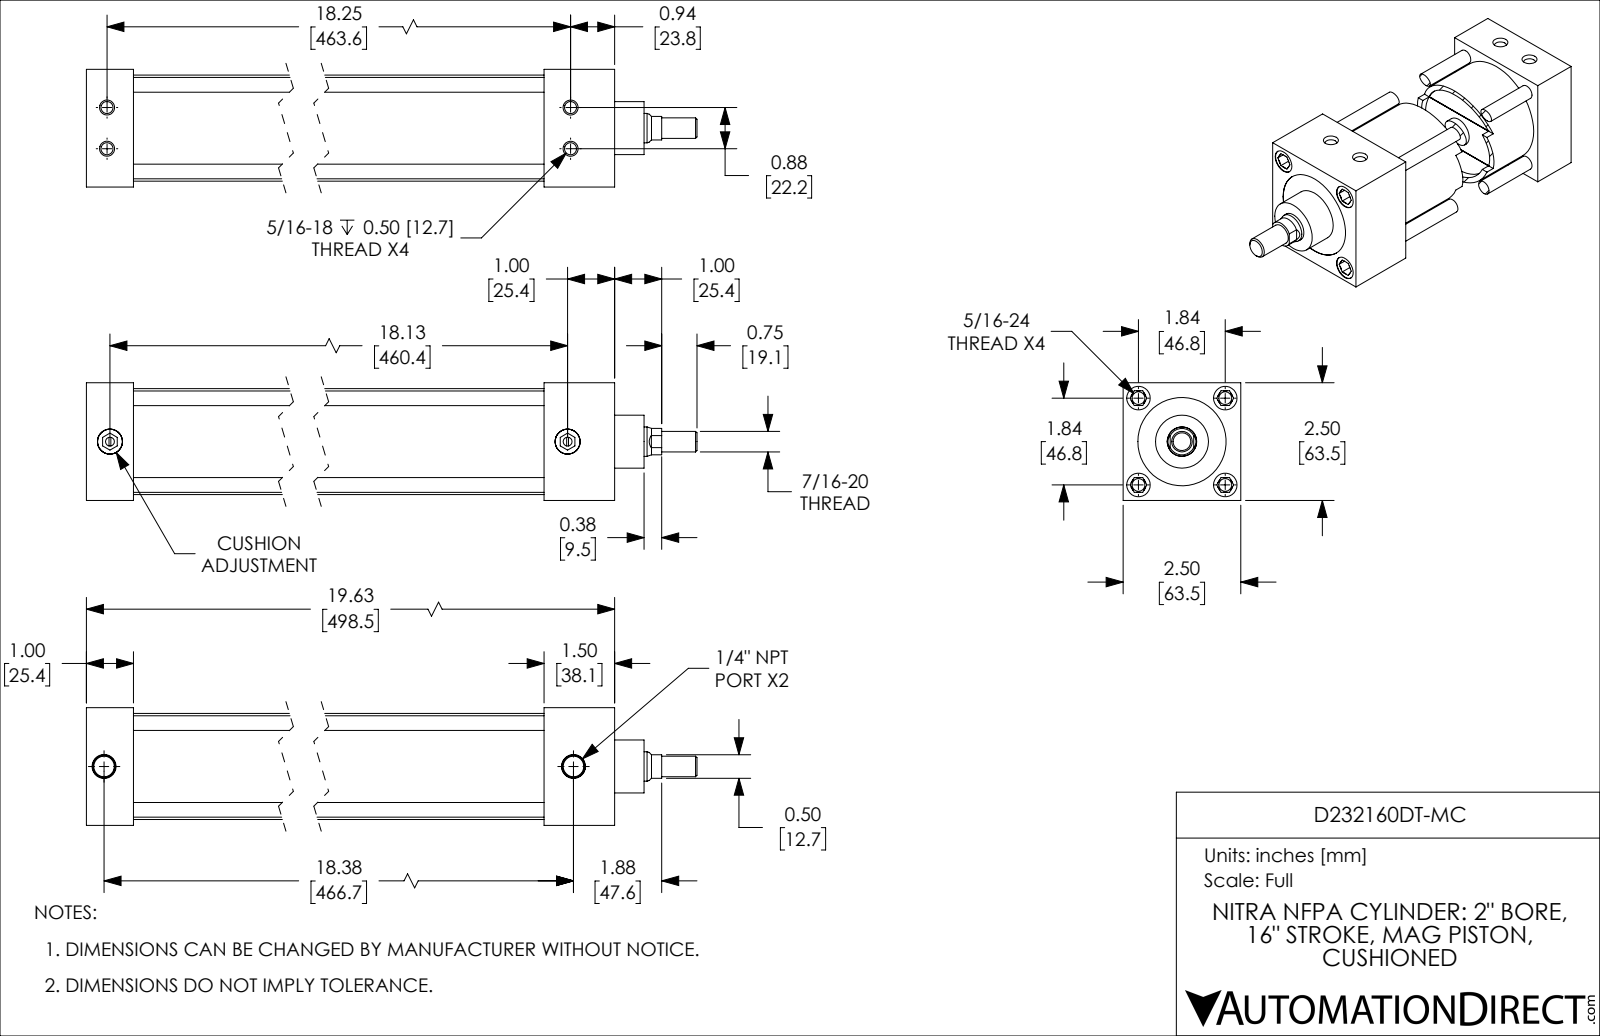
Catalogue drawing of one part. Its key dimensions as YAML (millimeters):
part_name: "D232160DT-MC_PISTON_KK1; D232160DT-MC_BODY; D232160DT-MC_CUSHION; D232160DT-MC"
step_written_by: "SolidWorks 2019 (CONFIG_CONTROL_DESIGN)"
units: millimeters
bodies: {solids: 4, faces: 248, planar: 90, cylindrical: 78, other: 80}
overall_size: [542.9, 63.5, 63.5]
volume: 714000
surface_area: 265700
round_holes:
  - {diameter: 6.9, count: 7}
  - {diameter: 6.5, count: 4}
  - {diameter: 12.7, count: 4}
  - {diameter: 4.8, count: 2}
  - {diameter: 11.1, count: 2}
  - {diameter: 13.5, count: 2}
  - {diameter: 15.9, count: 1}
  - {diameter: 47.6, count: 1}
  - {diameter: 50.8, count: 1}
round_bosses_or_shafts:
  - {diameter: 7.9, count: 4}
  - {diameter: 13.5, count: 2}
  - {diameter: 57.2, count: 1}
  - {diameter: 50.8, count: 1}
  - {diameter: 28.6, count: 1}
  - {diameter: 15.8, count: 1}
  - {diameter: 11.1, count: 1}
partial_cylinders:
  - {radius: 7.1, count: 1}
face_to_face_distances: [63.5, 25.4, 460.4, 435, 54, 28.6, 406.4, 498.5, 473.1, 444.5]
hole_center_spacings: [46.7, 46.8, 33, 11.2, 11.3, 22.2, 33.1, 66.1]
